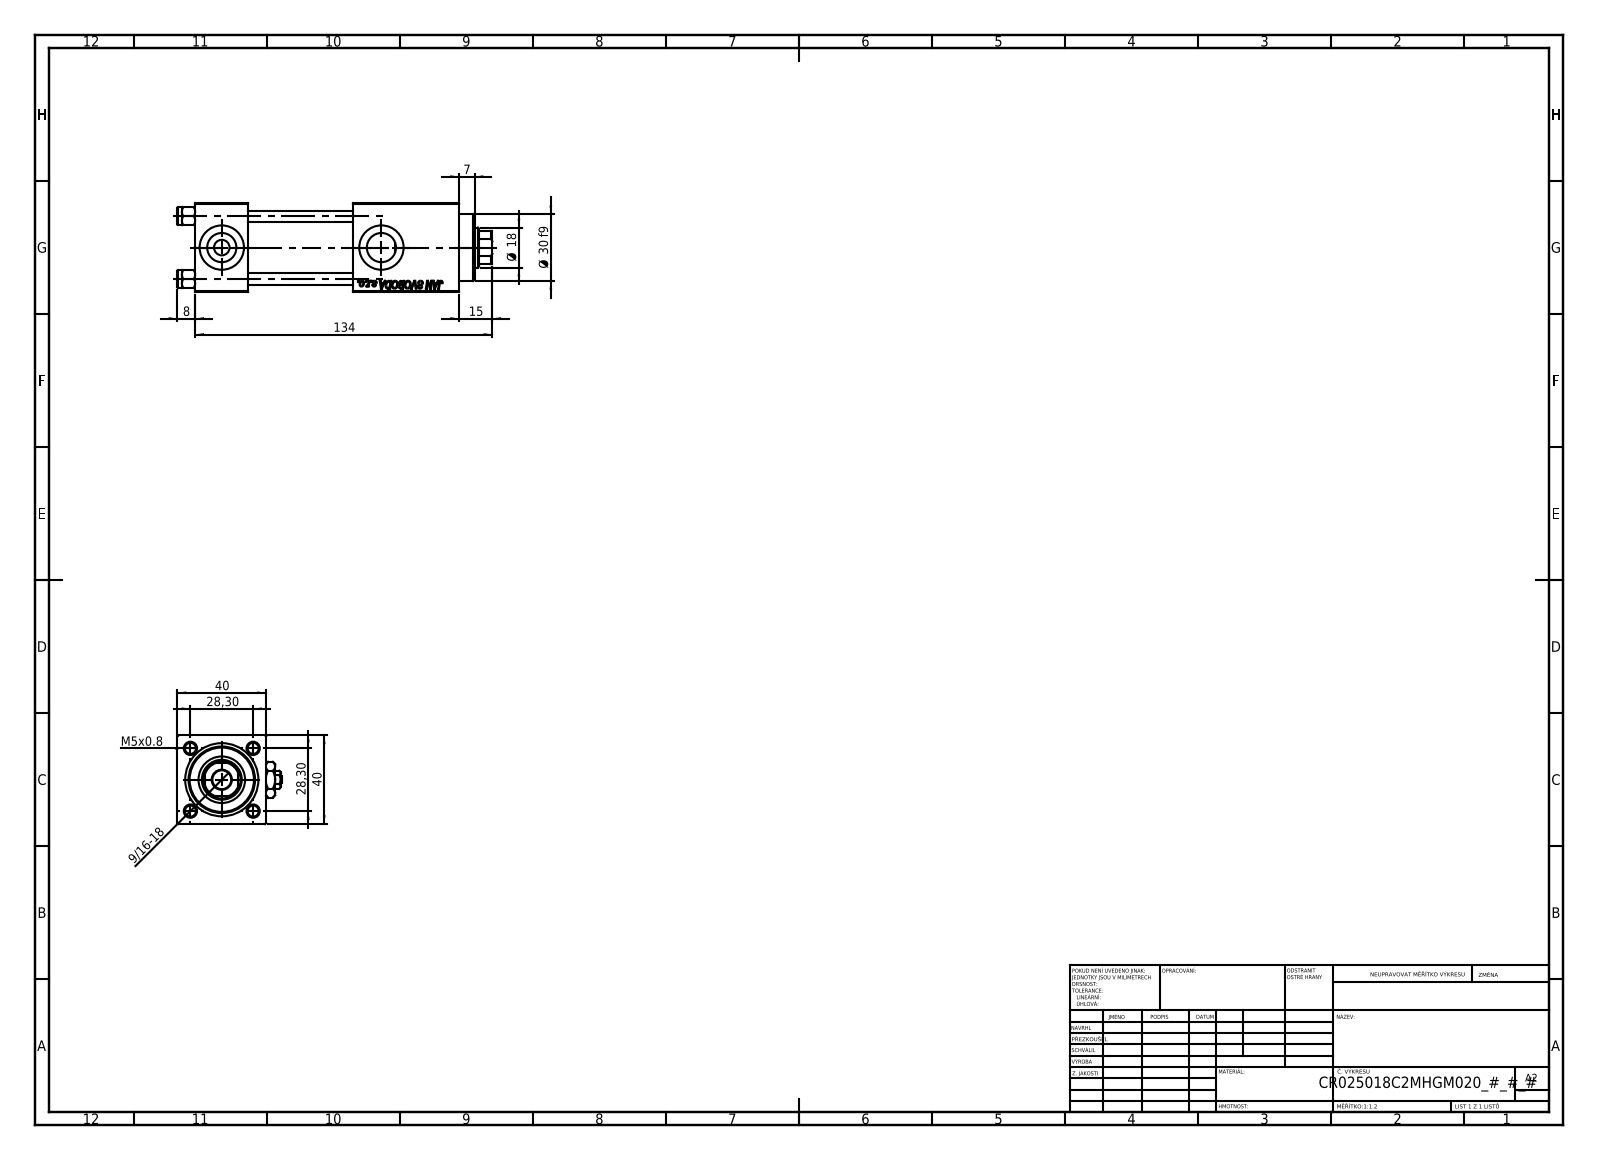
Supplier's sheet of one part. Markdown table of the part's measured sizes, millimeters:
| quantity | value |
| --- | --- |
| part name | NUT_M5_C; Zatka_pro_OIL_PORT; V215CR_C_TYCINKA; V215CR_C_Body (+2 more) |
| STEP written by | SolidWorks 2019 (CONFIG_CONTROL_DESIGN) |
| units | millimeters |
| bodies | 12 solids, 1197 faces (547 planar, 92 cylindrical, 558 other) |
| overall size | 142 × 47 × 40 |
| volume | 152 204 mm³ |
| surface area | 57 971 mm² |
| round holes (diameter × count) | 5 × 4, 20 × 3, 7 × 2, 13.16 × 2, 8.5 × 1, 18 × 1, 21 × 1, 25 × 1, 30 × 1 |
| round bosses / shafts (diameter × count) | 8 × 4, 31 × 1 |
| partial cylindrical surfaces (radius × count) | 8.5 × 1 |
| main face-to-face distances | 40, 24, 47, 71, 90.3, 66.3, 19.3, 48, 39.8, 119 |
| hole center spacings | 20.01, 28.3, 40.02, 72 |
